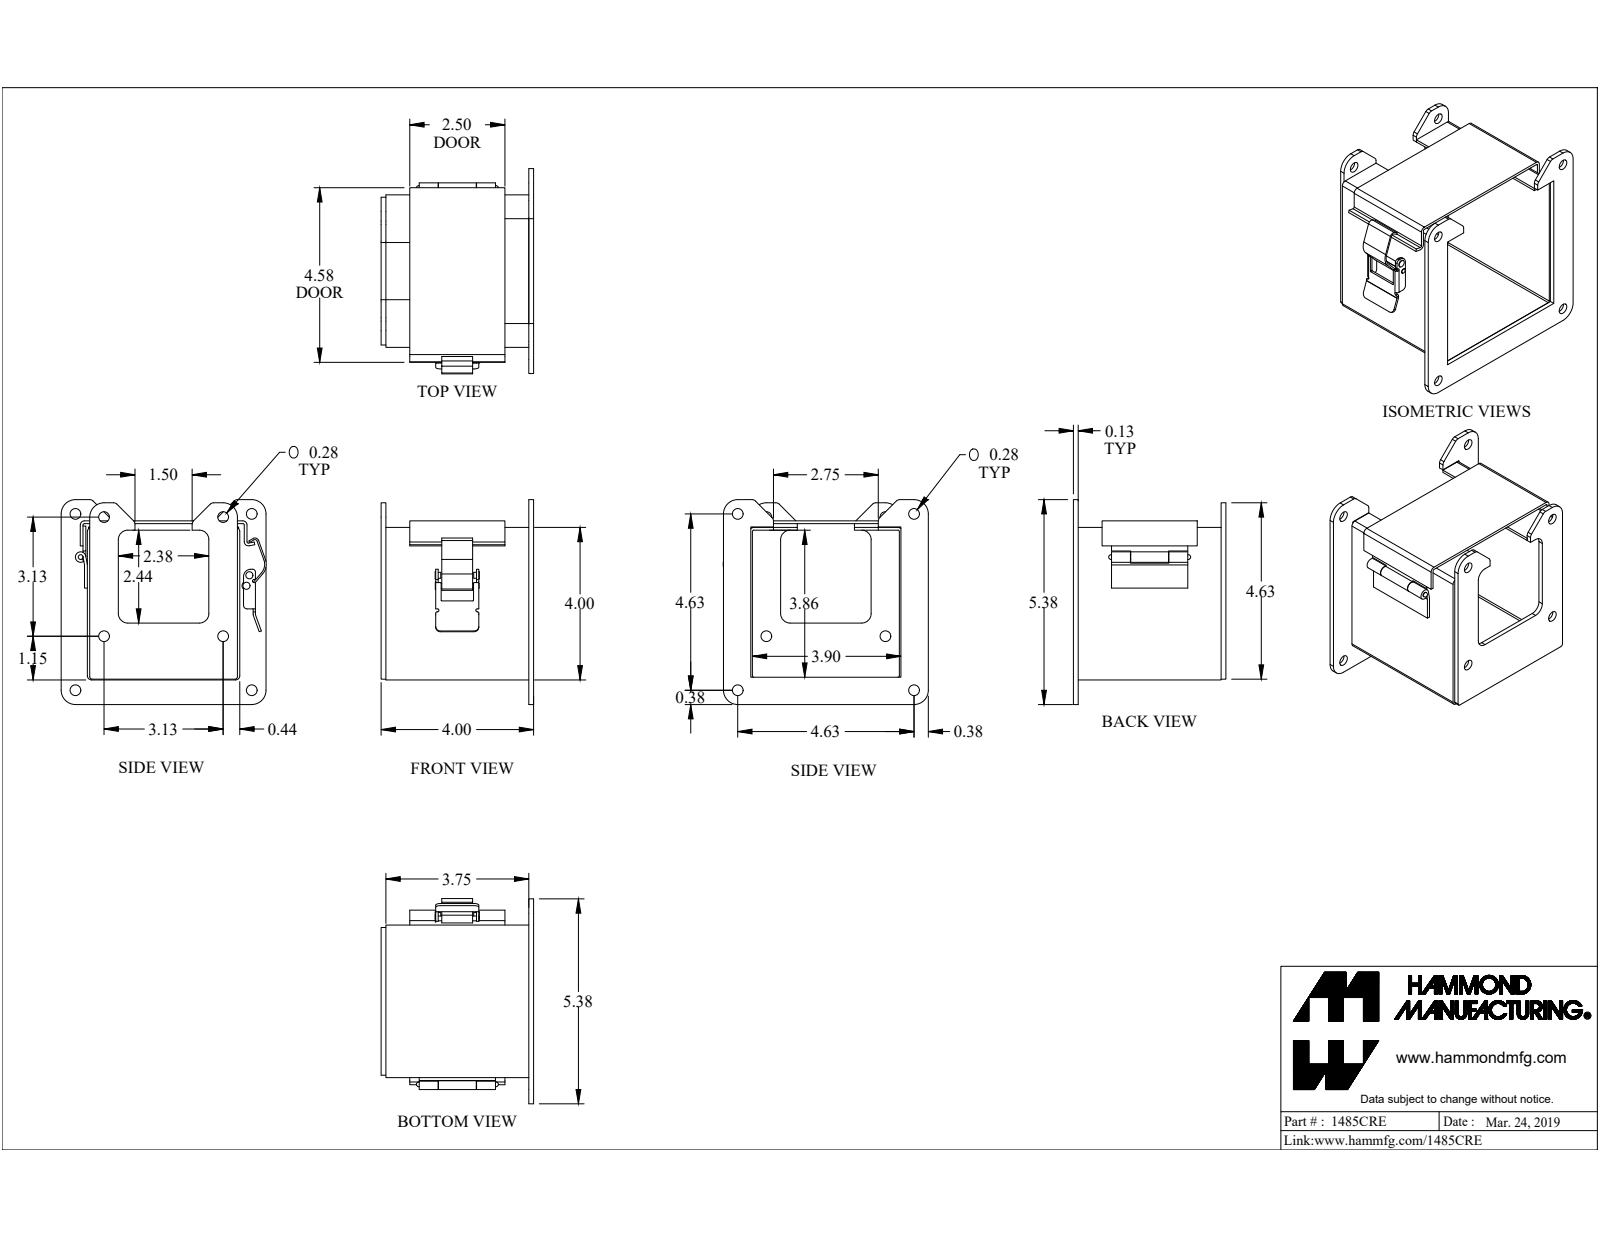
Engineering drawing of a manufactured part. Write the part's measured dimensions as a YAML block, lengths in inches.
part_name: "1485CRE"
step_written_by: "SolidWorks 2019 (CONFIG_CONTROL_DESIGN)"
units: inches
bodies: {solids: 10, faces: 249, planar: 146, cylindrical: 101, other: 2}
overall_size: [5.383, 5.375, 4]
volume: 7.878
surface_area: 203.4
round_holes:
  - {diameter: 0.281, count: 8}
  - {diameter: 0.125, count: 1}
  - {diameter: 0.125, count: 1}
  - {diameter: 0.13, count: 1}
  - {diameter: 0.164, count: 1}
round_bosses_or_shafts:
  - {diameter: 0.187, count: 2}
  - {diameter: 0.275, count: 1}
  - {diameter: 0.156, count: 1}
  - {diameter: 0.125, count: 1}
partial_cylinders:
  - {radius: 0.125, count: 11}
  - {radius: 0.016, count: 7}
  - {radius: 0.036, count: 7}
  - {radius: 0.108, count: 7}
  - {radius: 0.375, count: 6}
  - {radius: 0.25, count: 4}
  - {radius: 0.035, count: 3}
  - {radius: 0.039, count: 3}
face_to_face_distances: [0.072, 3.928, 4, 4.1, 3.856, 0.172, 3.875, 0.125, 3.75, 0.125]
hole_center_spacings: [0.755, 1.603, 3.125, 3.125, 3.294, 3.876, 4.126, 4.419]
